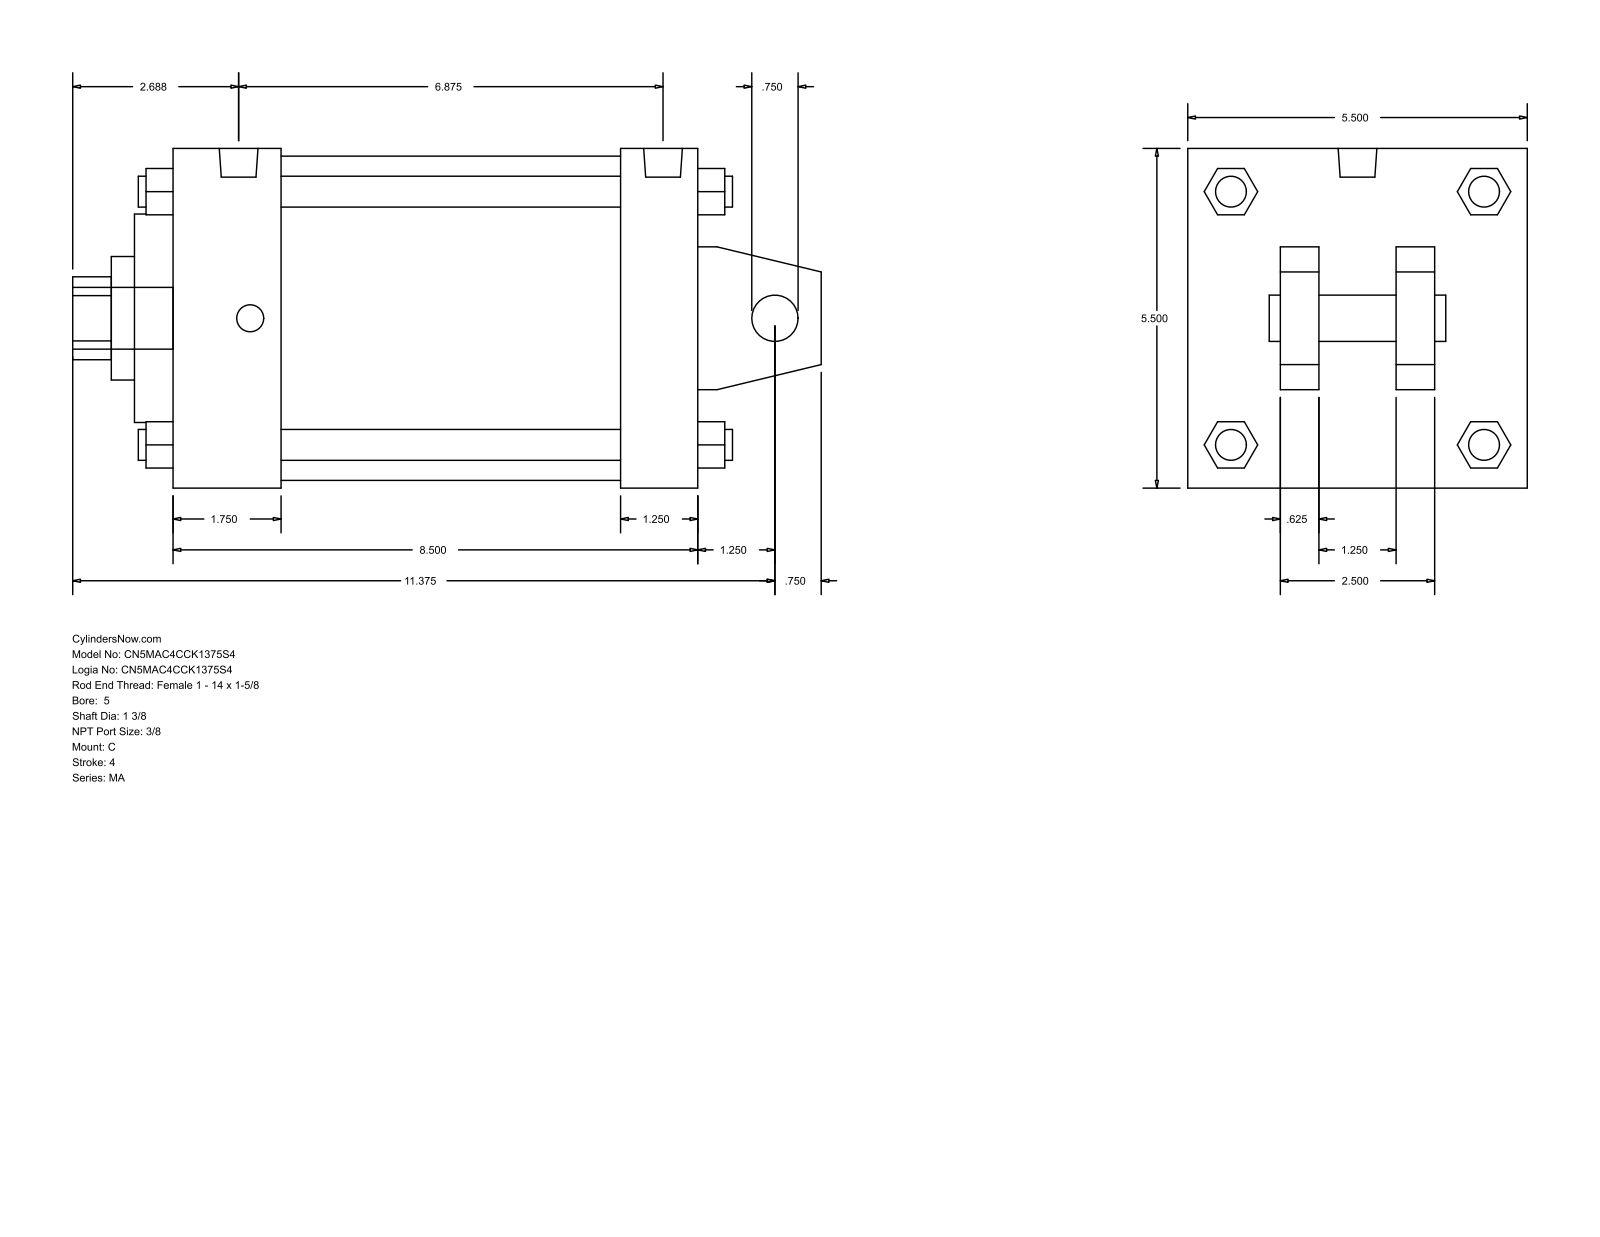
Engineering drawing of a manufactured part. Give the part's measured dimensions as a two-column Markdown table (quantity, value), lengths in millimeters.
| quantity | value |
| --- | --- |
| part name | MA_C__0500_1.375 |
| STEP written by | GSSL Pune (CONFIG_CONTROL_DESIGN) |
| units | millimeters |
| bodies | 0 solids, 141 faces (109 planar, 32 cylindrical, 0 other) |
| overall size | 307.98 × 139.7 × 139.7 |
| round holes (diameter × count) | 19.05 × 1, 34.92 × 1, 50.8 × 1, 85.72 × 1, 133.35 × 1 |
| round bosses / shafts (diameter × count) | 12.7 × 4, 11.11 × 4, 15.93 × 2, 25.4 × 1 |
| partial cylindrical surfaces (radius × count) | 17.06 × 1 |
| main face-to-face distances | 139.7, 215.91, 15.87, 184.16, 31.75, 44.45, 139.71, 171.46, 38.1, 101.6 |
